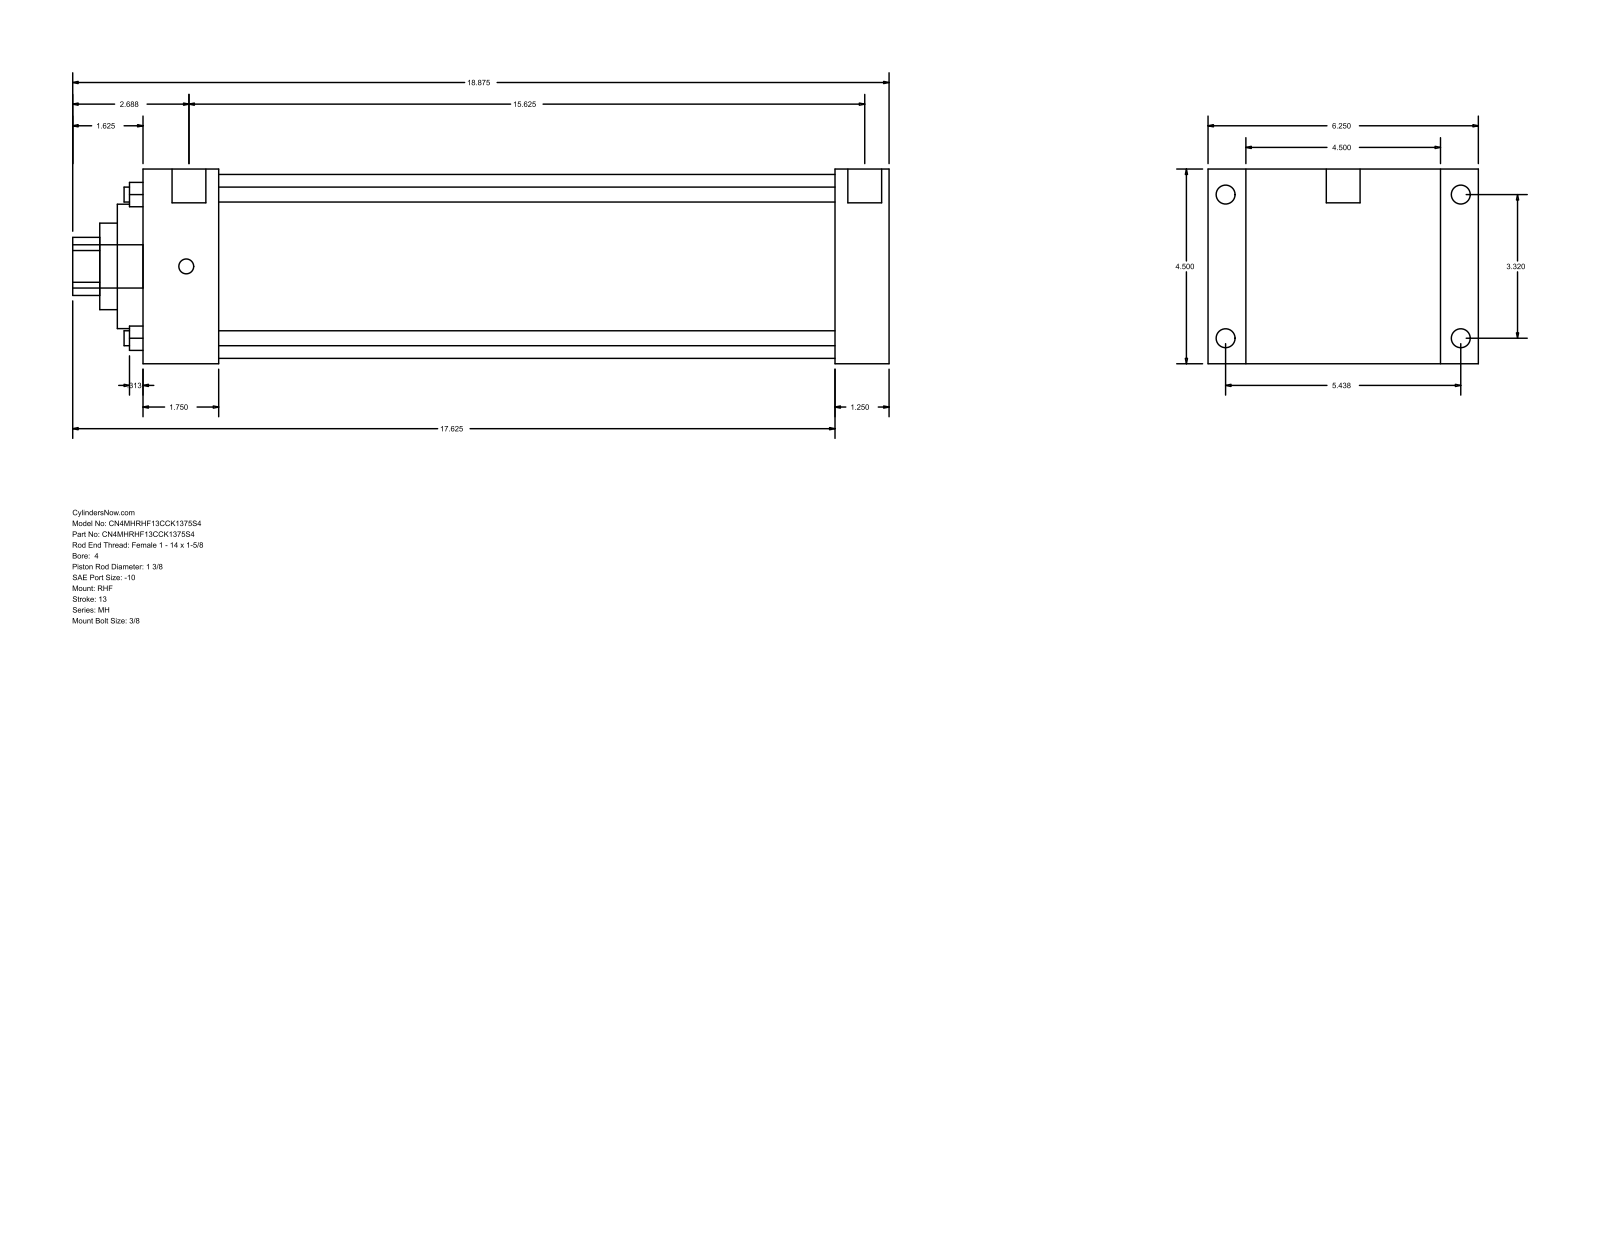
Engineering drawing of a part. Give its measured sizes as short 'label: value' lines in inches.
name: MH_RHF__0400_1.375
written by: GSSL Pune (CONFIG_CONTROL_DESIGN)
unit: in
bodies: 0 solids, 90 faces (61 planar, 29 cylindrical, 0 other)
size: 18.875 × 6.25 × 4.5
holes: 4× ⌀0.345, 1× ⌀1.375, 1× ⌀2, 1× ⌀2.875, 1× ⌀4.25
bosses: 4× ⌀0.438, 4× ⌀0.344, 2× ⌀0.781, 1× ⌀1
rounds: 1× R0.672
face distances: 4.5, 17.25, 16, 1.25, 0.875, 5.375, 1.75, 14.25, 15.5, 6.25
hole spacings: 2.347, 3.32, 4.695
